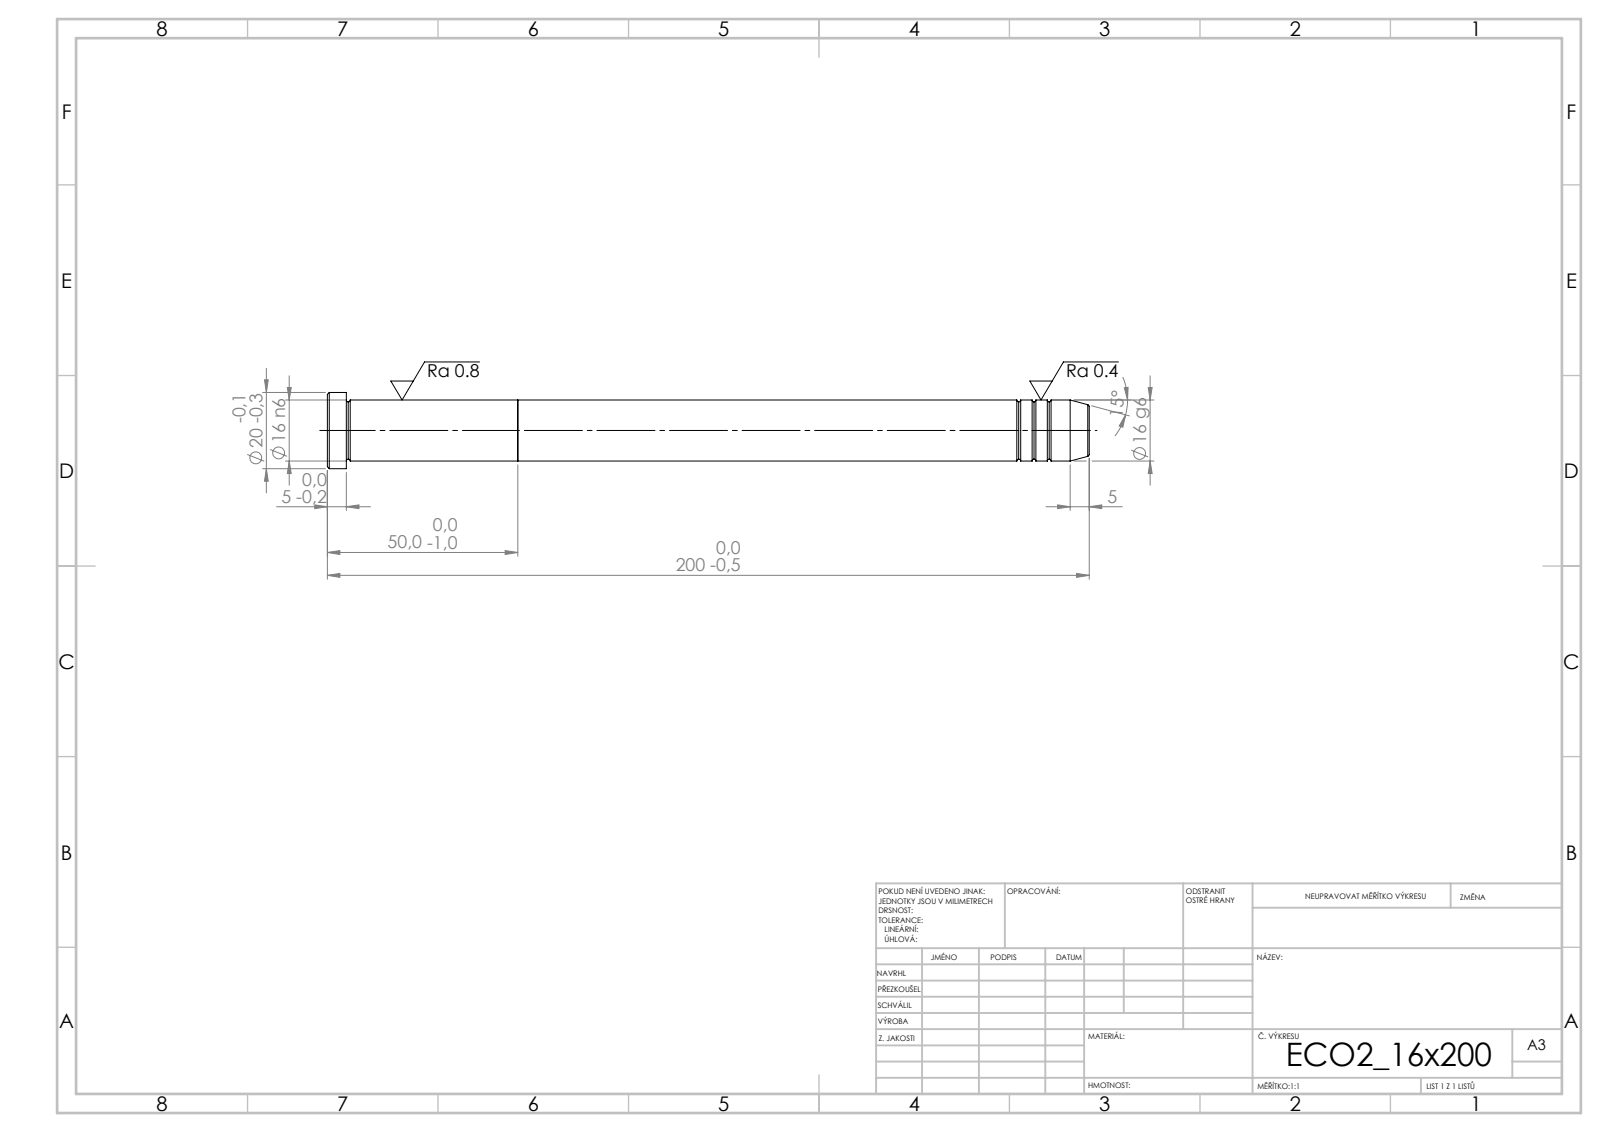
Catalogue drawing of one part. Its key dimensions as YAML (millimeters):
step_written_by: "SolidWorks 2019 (CONFIG_CONTROL_DESIGN)"
units: millimeters
bodies: {solids: 2, faces: 39, planar: 5, cylindrical: 12, other: 22}
overall_size: [200, 20, 20]
volume: 40533
surface_area: 11150
round_bosses_or_shafts:
  - {diameter: 20, count: 1}
  - {diameter: 16, count: 1}
face_to_face_distances: [50, 150, 200, 195, 45, 5]
